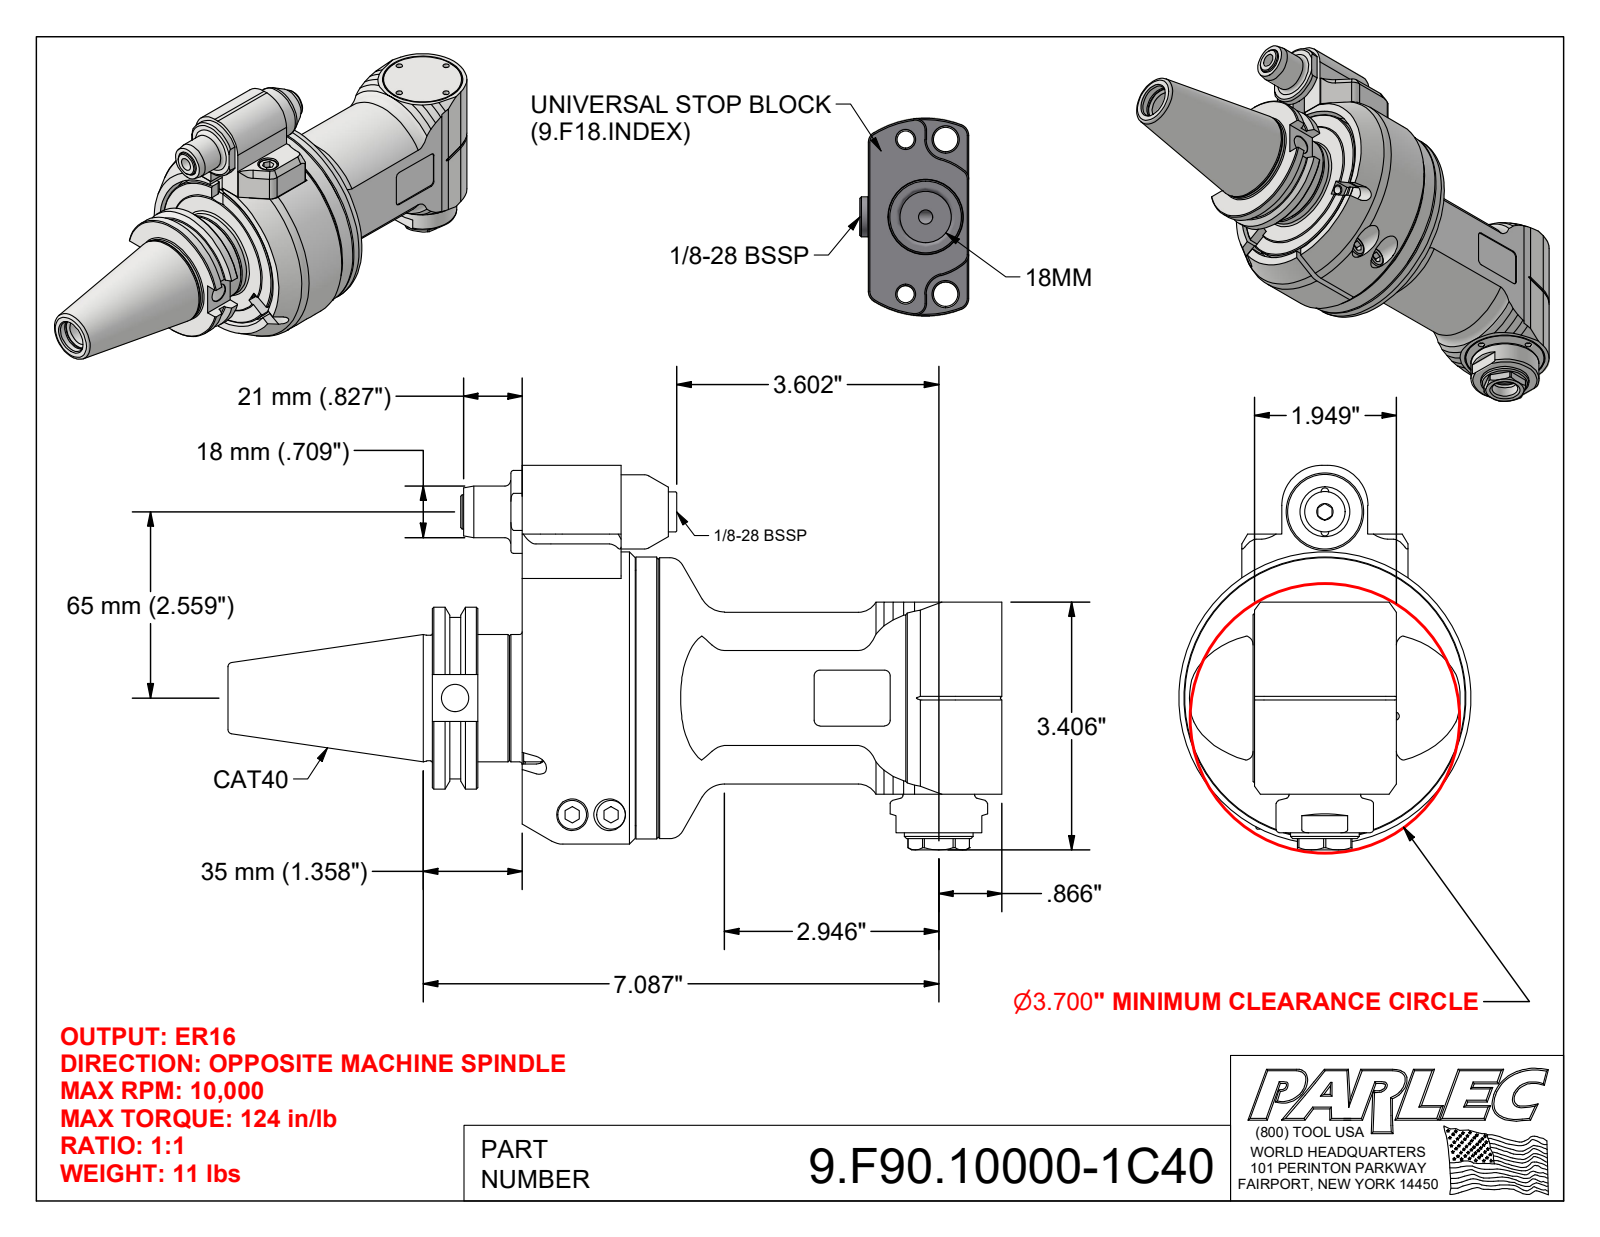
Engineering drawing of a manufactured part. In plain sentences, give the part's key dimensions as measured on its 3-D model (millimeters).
The part is named "9.F90.10000-1C40; 9_F90_10000; 9_GA1_448_2 (Type 1, Cat40, 65mm)". Its 3-D file was written by "Autodesk Inventor 2022 (AUTOMOTIVE_DESIGN)". It is 5 solids with 591 faces: 241 planar, 158 cylindrical and 192 other. Overall it measures 270.3 by 134.2 by 102 millimeters. Its volume is 904 600 cubic millimeters and its surface area 146 600 square millimeters. Round holes: 20 of diameter 8.5, 4 of diameter 1.6, 4 of diameter 2, 4 of diameter 3.2, 3 of diameter 11, 2 of diameter 2.6, 2 of diameter 4.2, 2 of diameter 5, 2 of diameter 10.4, 2 of diameter 12, 2 of diameter 13, 1 of diameter 2.5. Round bosses or shafts: 4 of diameter 10, 4 of diameter 6, 2 of diameter 8, 2 of diameter 2.5, 1 of diameter 102, 1 of diameter 98.4, 1 of diameter 98, 1 of diameter 77. Partial cylindrical surfaces (rounded edges, fillets, slot ends): 12 of radius 2, 4 of radius 4, 2 of radius 0.4, 2 of radius 0.5, 2 of radius 1, 2 of radius 3.5, 2 of radius 5, 2 of radius 14. The main face-to-face distances are 0.5, 39.5, 32, 7, 8.5, 7.5, 1, 31, 26, 50. The hole center spacings are 38.5, 76.3, 46.3, 10.7, 54.5, 74, 77, 31.3.
